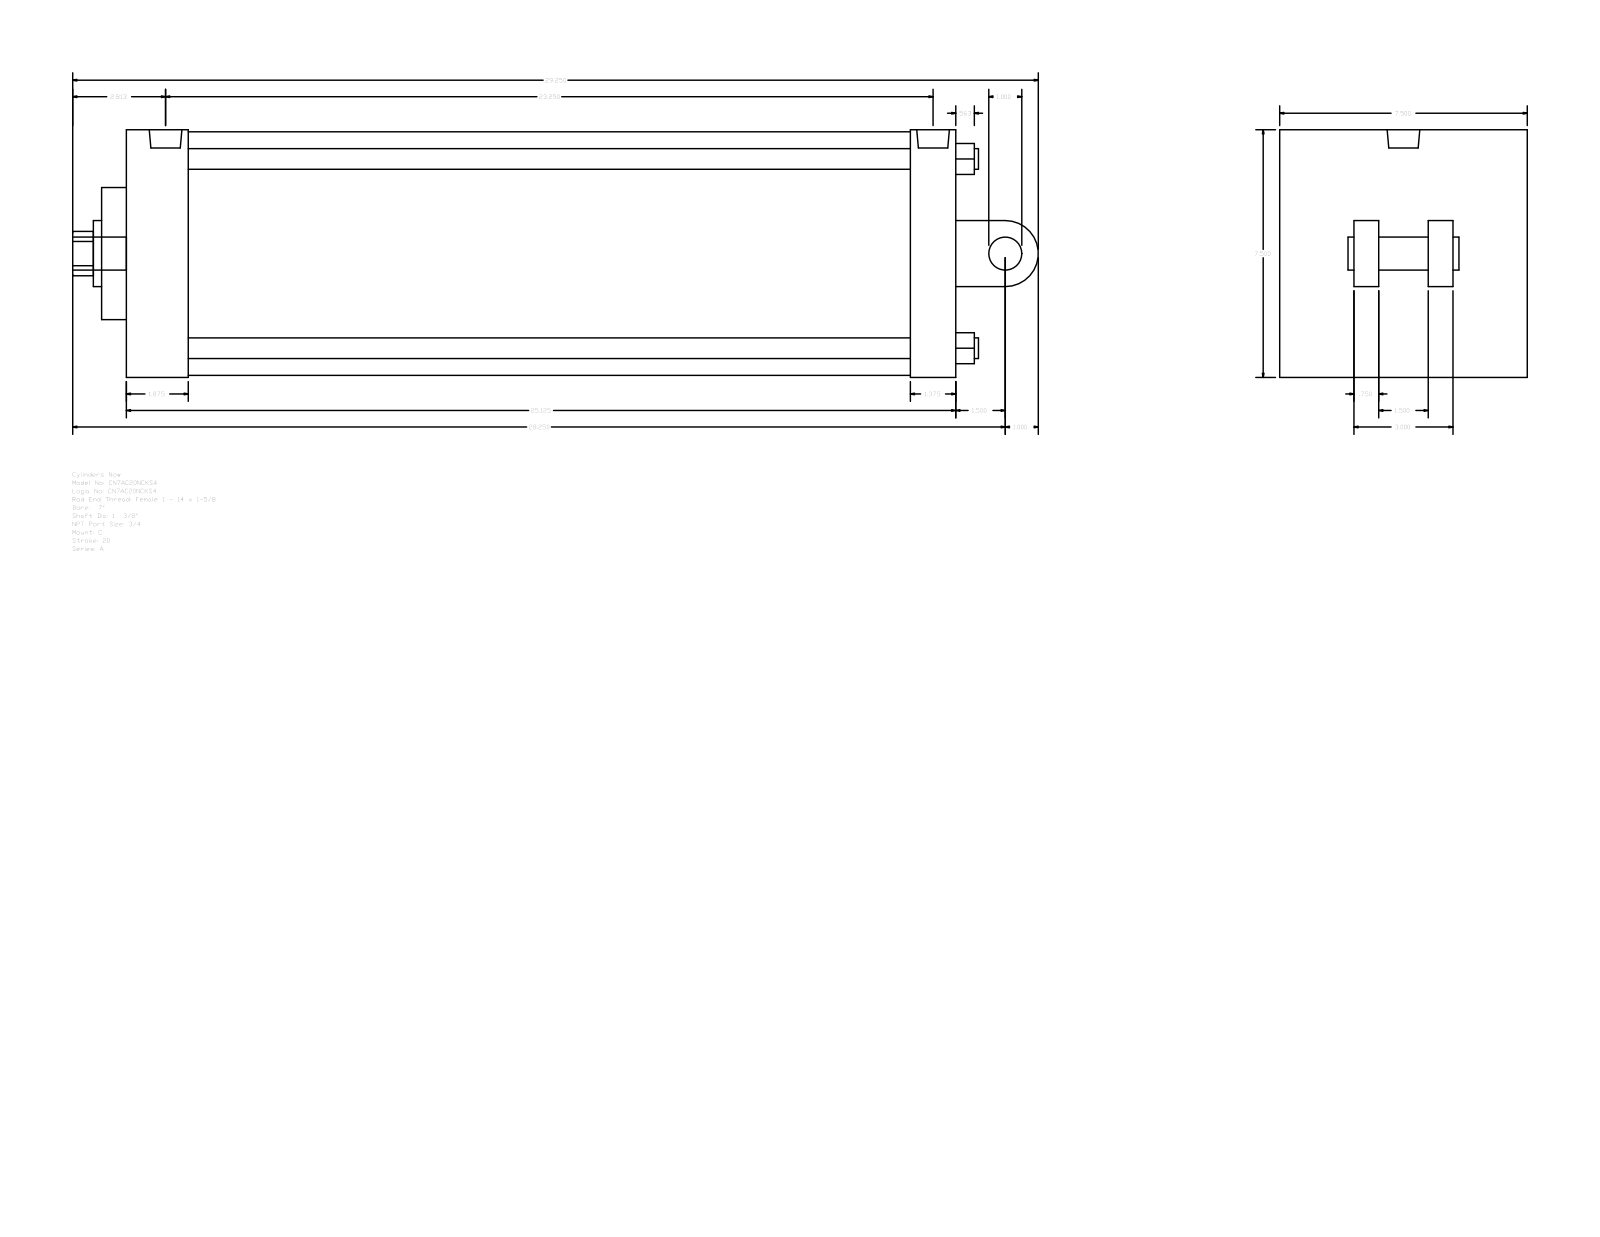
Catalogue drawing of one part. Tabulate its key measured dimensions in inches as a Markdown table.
| quantity | value |
| --- | --- |
| part name | A_C__0700_1.375 |
| STEP written by | GSSL Pune (CONFIG_CONTROL_DESIGN) |
| units | inches |
| bodies | 0 solids, 104 faces (75 planar, 29 cylindrical, 0 other) |
| overall size | 29.25 × 7.5 × 7.5 |
| round holes (diameter × count) | 0.625 × 4, 0.594 × 2, 0.989 × 1, 1.375 × 1, 2 × 1, 7.375 × 1 |
| round bosses / shafts (diameter × count) | 1 × 2, 0.594 × 2, 0.989 × 1 |
| partial cylindrical surfaces (radius × count) | 0.672 × 1, 1 × 1 |
| main face-to-face distances | 7.5, 25.125, 3, 2.25, 0.75, 25.875, 2.625, 1.875, 23.25, 24.5 |
| hole center spacings | 4.052, 5.73, 8.103, 0.219 |
